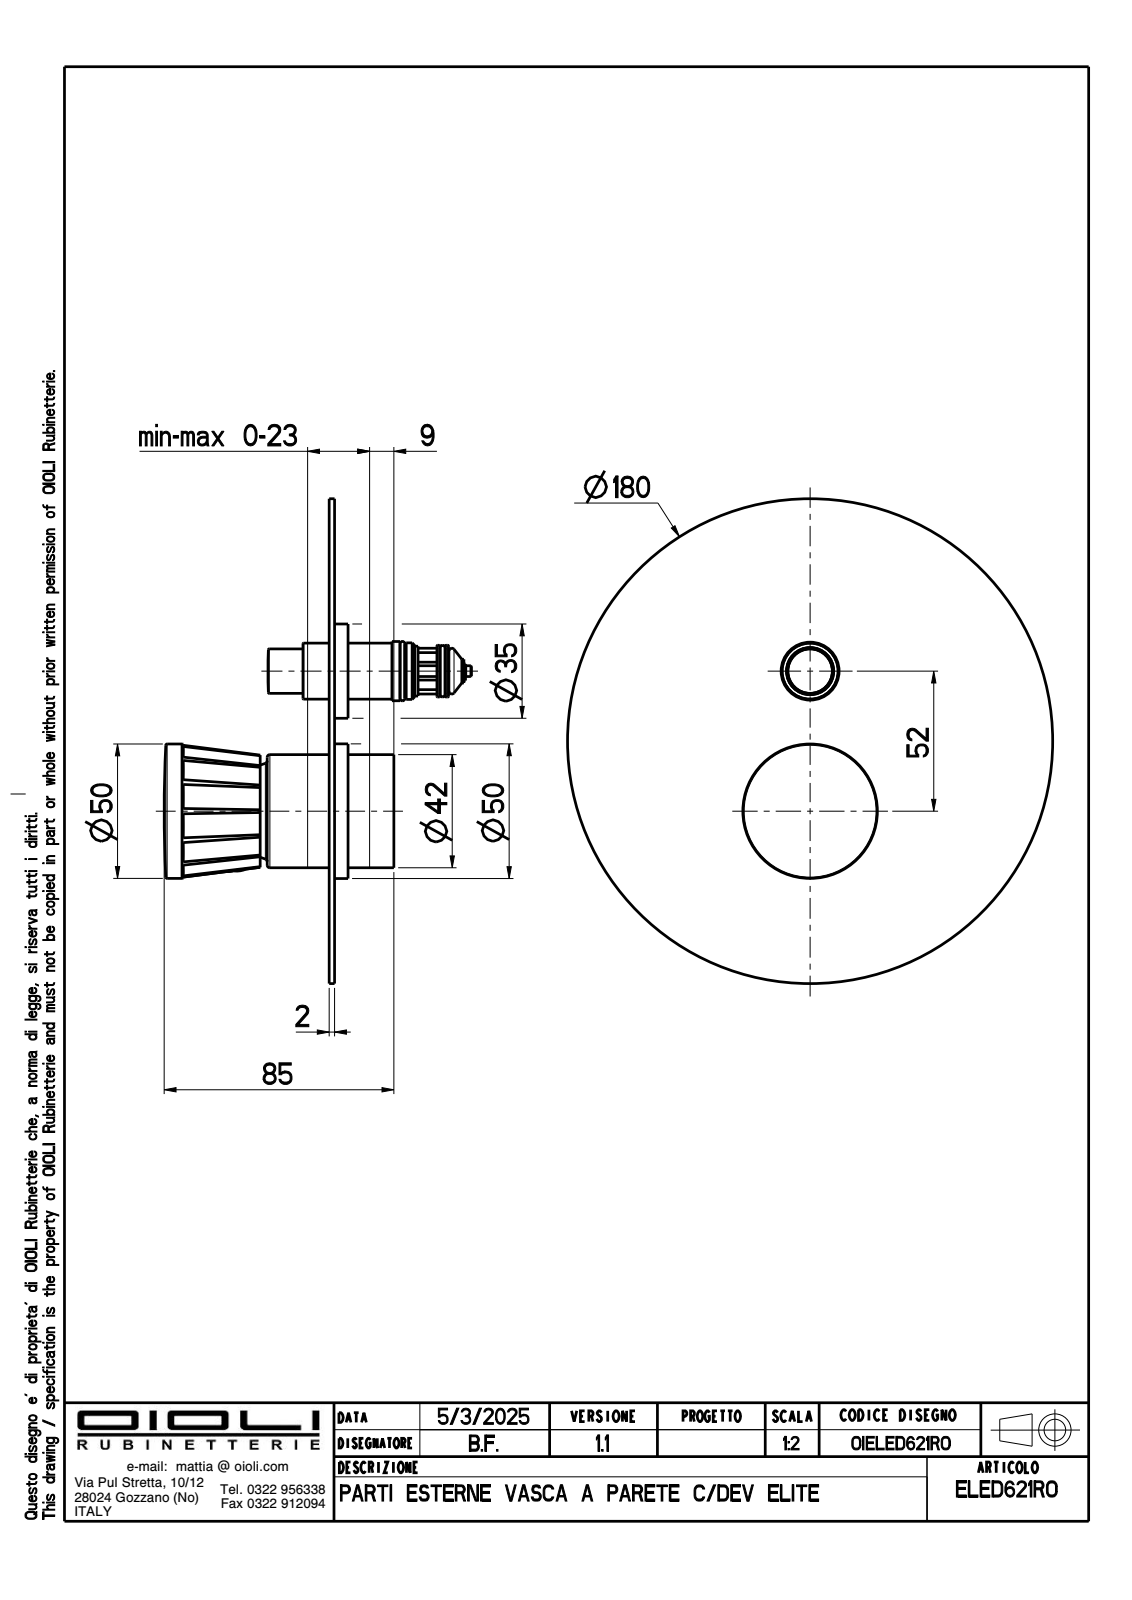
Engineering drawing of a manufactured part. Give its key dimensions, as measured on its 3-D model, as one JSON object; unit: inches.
{"part_name": "OIBR00949; OILT00033; OIBR00948; OIAQ00013 (+3 more)", "step_written_by": "CREO PARAMETRIC BY PTC INC, 2024493 (CONFIG_CONTROL_DESIGN)", "units": "inches", "bodies": {"solids": 6, "faces": 190, "planar": 66, "cylindrical": 64, "other": 60}, "overall_size": [7.087, 7.087, 3.355], "volume_in3": 5.25, "surface_area_in2": 131.5, "round_holes": [[0.13, 1], [0.157, 1], [0.165, 1], [0.209, 1], [0.256, 1], [0.374, 1], [0.571, 1], [0.689, 1], [0.709, 1], [0.846, 1], [1.181, 1], [1.555, 1]], "round_bosses_or_shafts": [[0.65, 2], [7.087, 1], [1.965, 1], [1.654, 1], [0.819, 1], [0.748, 1], [0.236, 1], [0.197, 1]], "partial_cylinders_radius": [[0.004, 10], [0.268, 2]], "face_to_face_distances": [0.079, 2.366, 2.287, 0.669, 0.591, 1.697, 0.984, 0.906, 0.315, 1.382], "hole_center_spacings": [2.047]}
